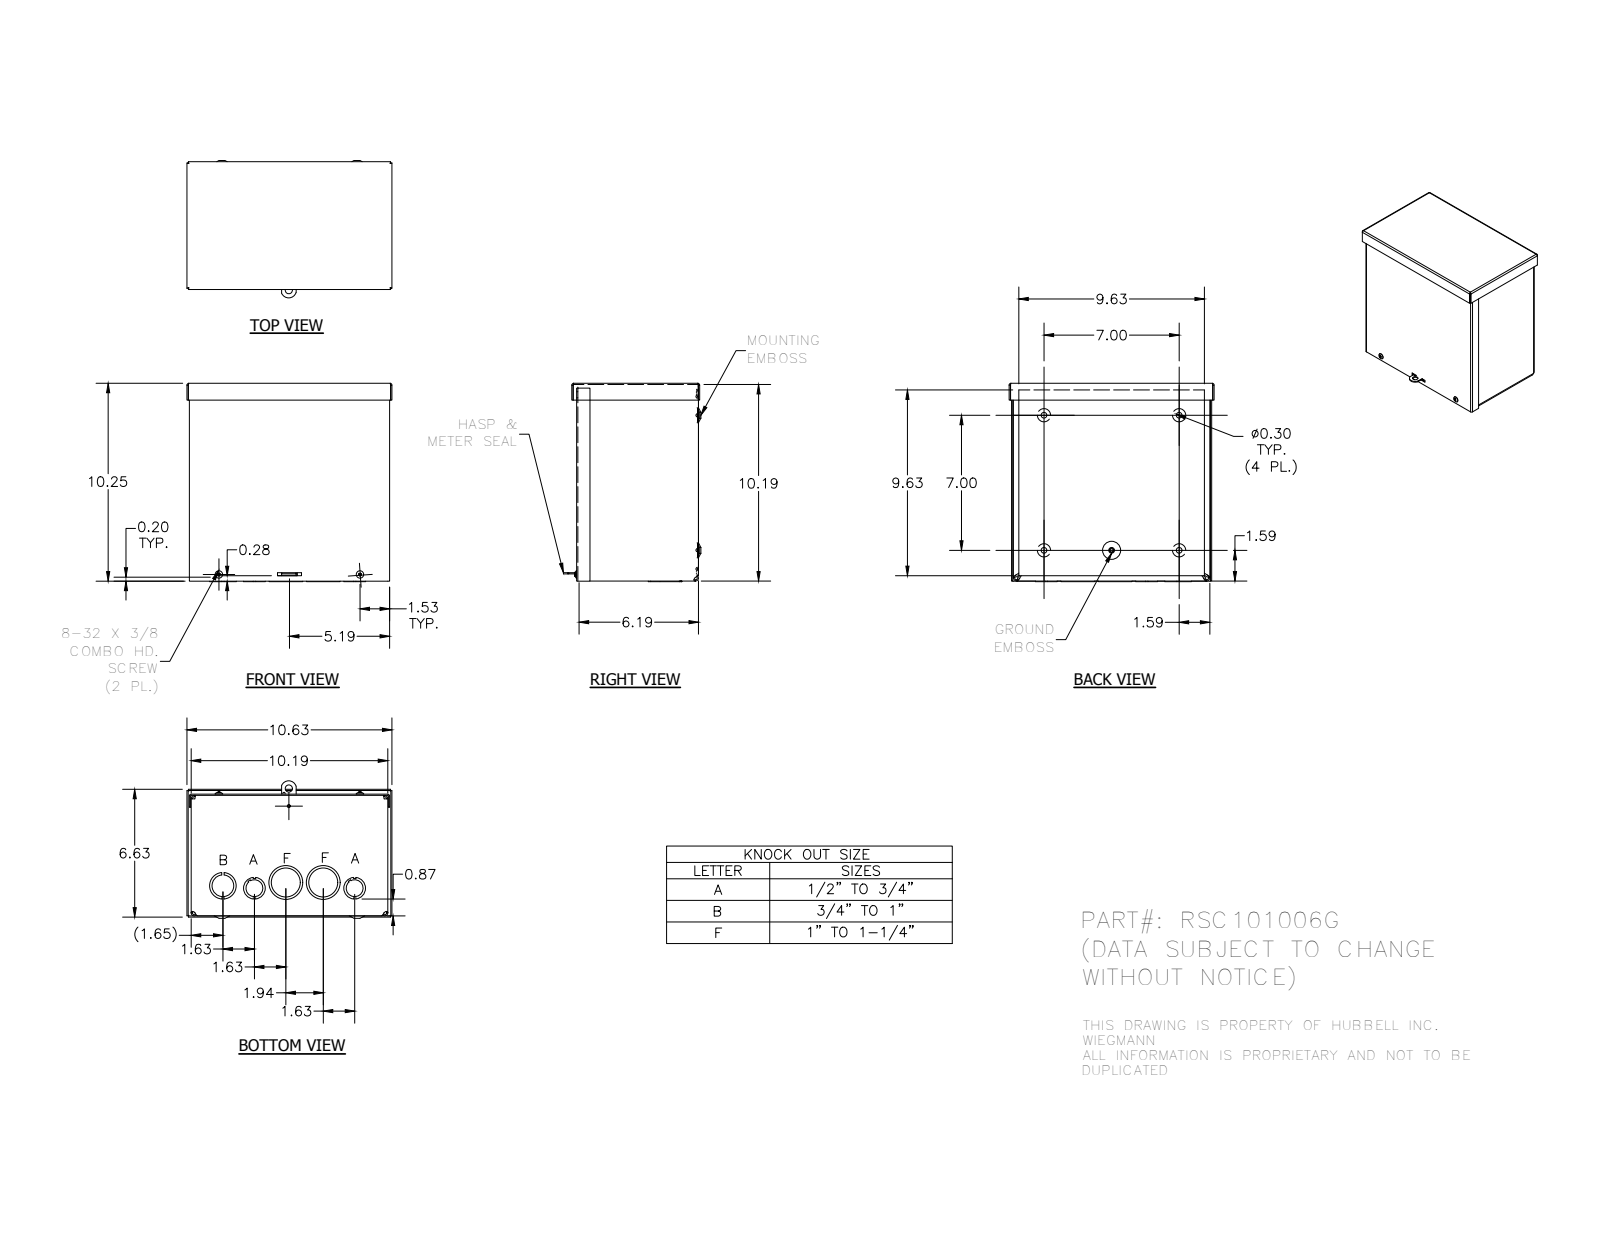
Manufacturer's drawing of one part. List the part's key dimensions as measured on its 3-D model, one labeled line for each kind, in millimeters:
Part name (STEP PRODUCT): RSC101006G_WRAP; RSC1010G_LID; RSC1006G_CAP; 3183 (+4 more)
STEP written by: Autodesk Inventor 2014 (AUTOMOTIVE_DESIGN)
Units: millimetres
Bodies: 7 solids, 518 faces (245 planar, 129 cylindrical, 144 other)
Overall size (bounding box): 269.88 × 261.12 × 180.97
Volume: 621 963 mm³ · Surface area: 800 856 mm²
Round holes (diameter × count): ⌀7.62 ×4, ⌀7.95 ×4, ⌀28.57 ×3, ⌀3.17 ×2, ⌀3.76 ×2, ⌀22.22 ×2, ⌀38.1 ×2, ⌀44.45 ×2, ⌀3.96 ×1, ⌀4.19 ×1, ⌀9.52 ×1, ⌀34.92 ×1
Round bosses / shafts (diameter × count): ⌀9.75 ×2, ⌀4.17 ×2, ⌀5.8 ×1
Partial cylindrical surfaces — rounded edges, fillets, slot ends (radius × count): R0.25 ×10, R0.79 ×8, R2.37 ×8, R3.17 ×8, R4.75 ×8, R0.79 ×4, R1.4 ×4, R1.57 ×4
Main face-to-face distances: 1.58, 257.19, 1.57, 158.73, 258.77, 157.15, 1.59, 3.15, 160.32, 158.74
Hole centre spacings: 177.8, 27.24, 32.03, 42.07, 88.9, 90.99, 185.75, 198.78
